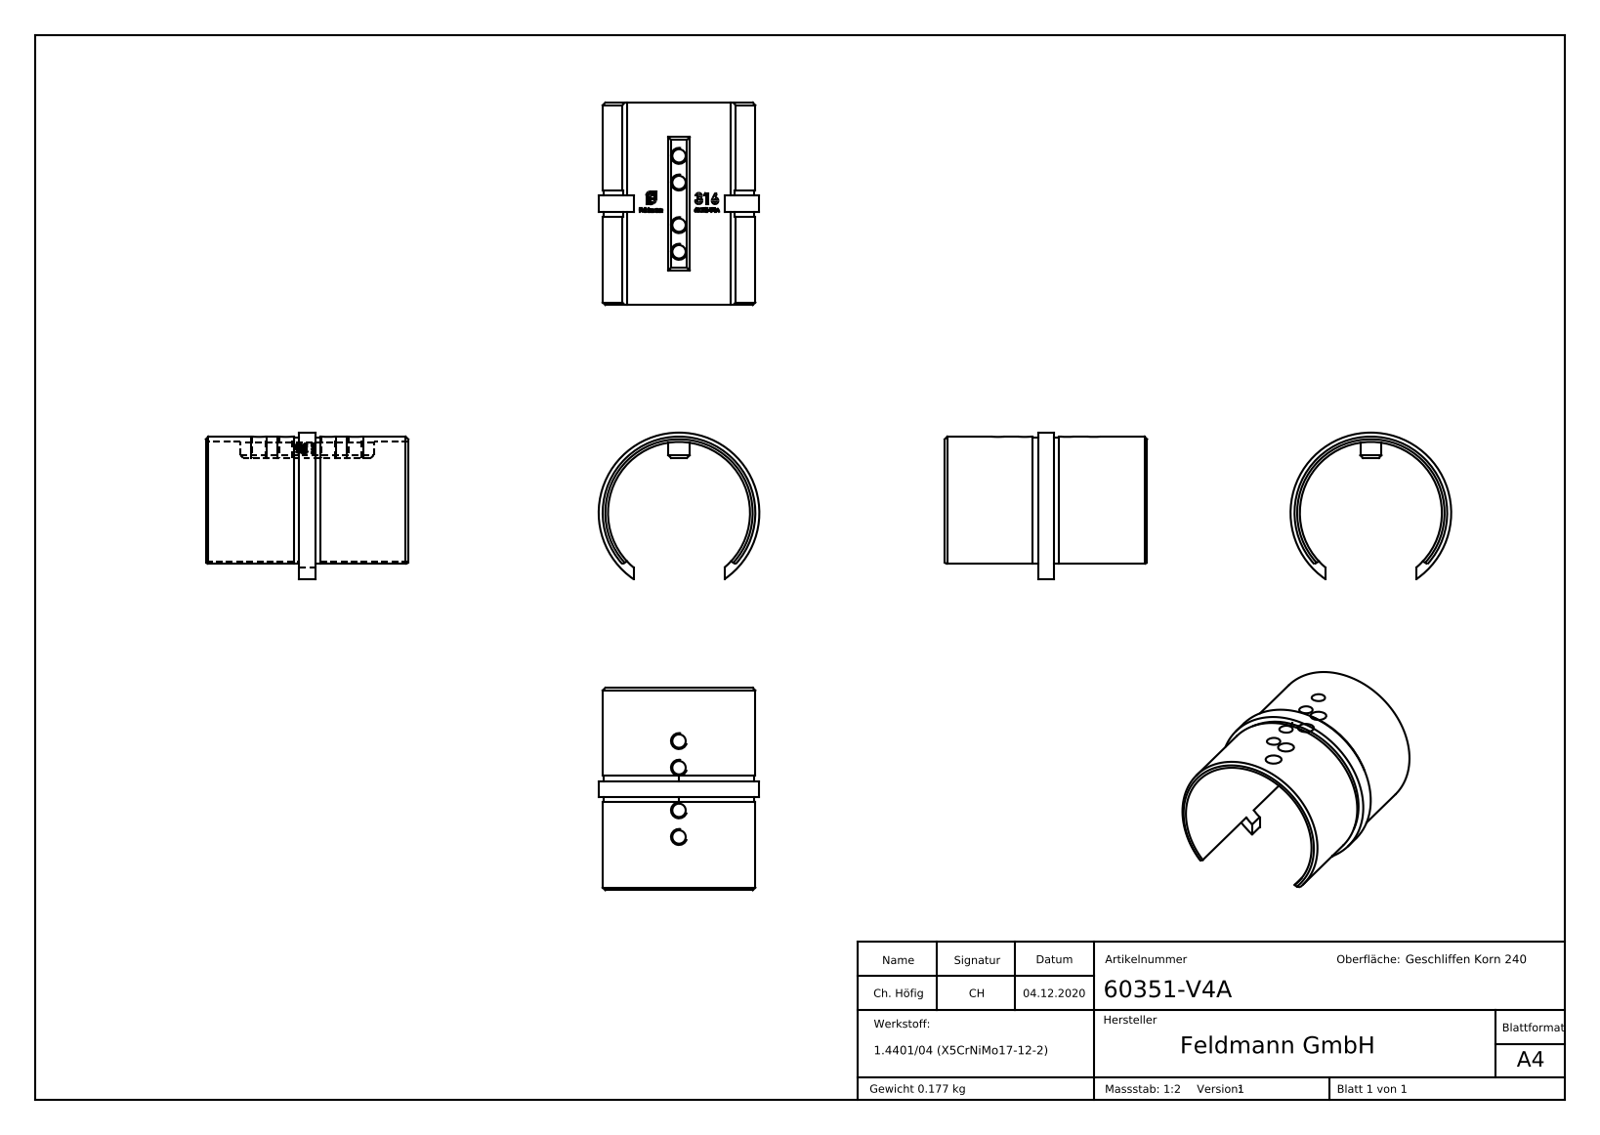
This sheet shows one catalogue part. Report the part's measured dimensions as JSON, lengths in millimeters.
{"part_name": "60351-V4A", "step_written_by": "SolidWorks 2018 (CONFIG_CONTROL_DESIGN)", "units": "millimeters", "bodies": {"solids": 1, "faces": 352, "planar": 162, "cylindrical": 55, "other": 135}, "overall_size": [76, 60.3, 55.05], "volume_mm3": 22165, "surface_area_mm2": 21985, "round_holes": [[5, 4]], "round_bosses_or_shafts": [[60.3, 1]], "partial_cylinders_radius": [[26.65, 1], [26.75, 1], [28.15, 1], [28.65, 1]], "face_to_face_distances": [8, 6, 35, 41, 33, 43, 2, 13, 76, 63], "hole_center_spacings": [10, 26, 16, 36]}
